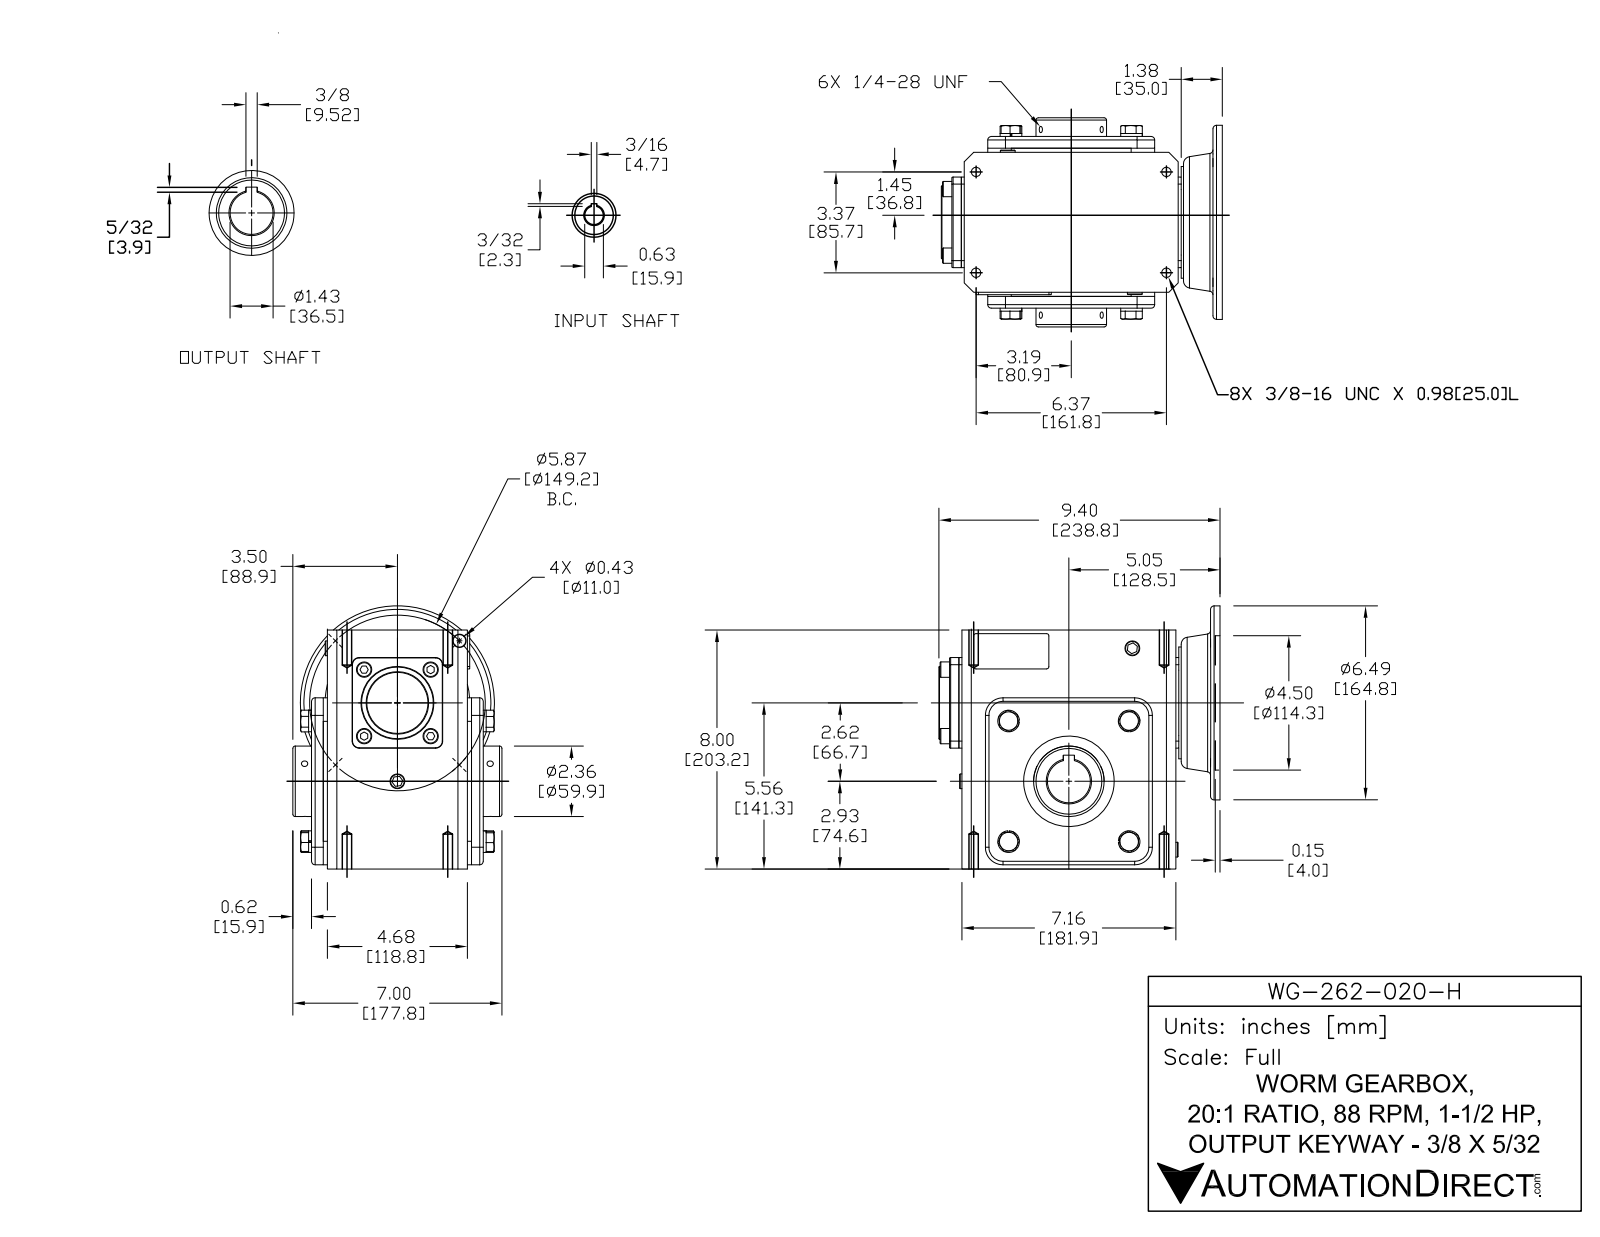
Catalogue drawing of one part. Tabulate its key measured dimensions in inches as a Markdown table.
| quantity | value |
| --- | --- |
| part name | WG-262-020-H |
| STEP written by | SolidWorks 2015 (CONFIG_CONTROL_DESIGN) |
| units | inches |
| bodies | 37 solids, 558 faces (306 planar, 156 cylindrical, 96 other) |
| overall size | 9.409 × 8.811 × 7 |
| volume | 310.4 in³ |
| surface area | 663.9 in² |
| round holes (diameter × count) | 0.213 × 6, 0.313 × 4, 0.406 × 4, 0.591 × 1, 0.625 × 1, 1.437 × 1, 1.457 × 1, 2.362 × 1, 3.031 × 1, 3.819 × 1, 4.5 × 1 |
| round bosses / shafts (diameter × count) | 0.724 × 4, 0.512 × 4, 6.496 × 1, 3.74 × 1, 2.441 × 1, 2.047 × 1, 1.181 × 1, 1.142 × 1 |
| partial cylindrical surfaces (radius × count) | 0.079 × 8, 0.118 × 8, 0.236 × 4, 0.591 × 4, 0.787 × 4, 0.02 × 2, 0.039 × 2 |
| main face-to-face distances | 4.961, 0.394, 0.098, 5.217, 5.354, 0.138, 4.823, 0.531, 7.264, 8 |
| hole center spacings | 2.937, 3.489, 4.154, 5.757, 6.213, 2.148, 3.375, 5.14 |
